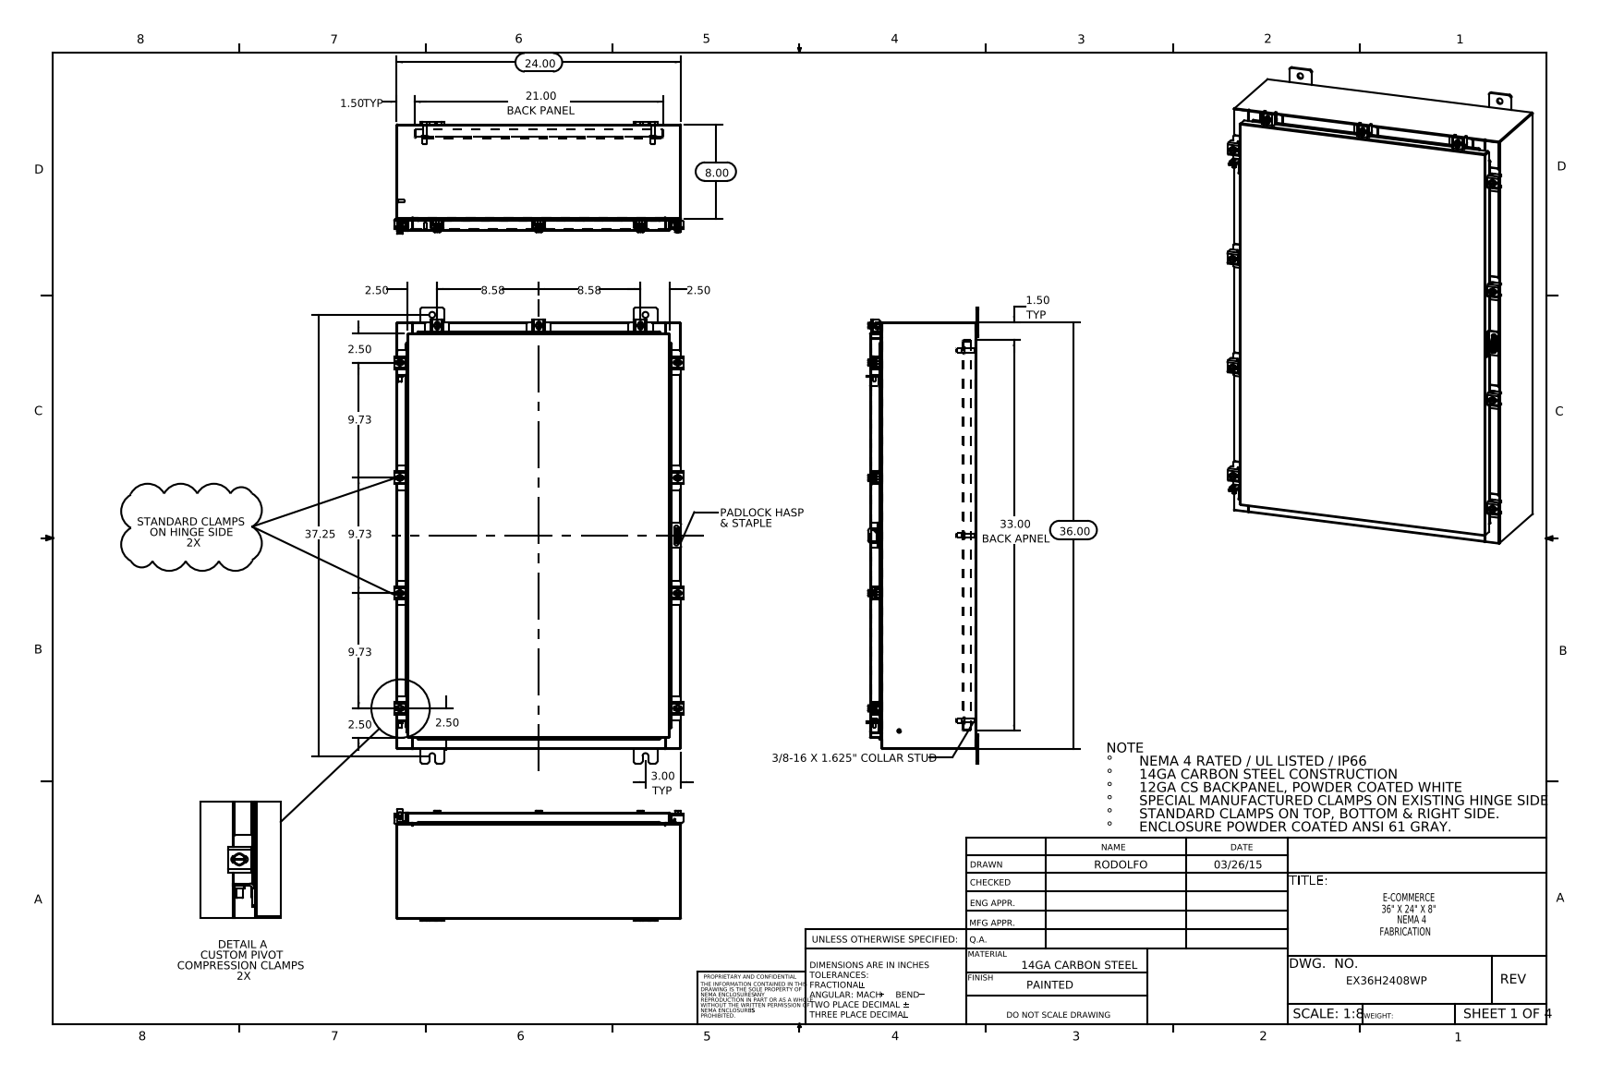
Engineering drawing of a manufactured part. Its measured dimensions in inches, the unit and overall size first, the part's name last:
Units: inches
Overall size (bounding box): 38.5 × 24.421 × 9.453
Round holes (diameter × count): ⌀0.213 ×11, ⌀0.26 ×11, ⌀0.5 ×10, ⌀0.125 ×1, ⌀0.25 ×1
Round bosses / shafts (diameter × count): ⌀0.5 ×11, ⌀0.25 ×11, ⌀0.399 ×9, ⌀0.625 ×6, ⌀0.375 ×6, ⌀0.33 ×6, ⌀0.315 ×2, ⌀0.236 ×2
Partial cylindrical surfaces — rounded edges, fillets, slot ends (radius × count): R0.06 ×48, R0.013 ×26, R0.19 ×24, R0.088 ×22, R0.141 ×22, R0.09 ×20, R0.12 ×20, R0.05 ×19
Main face-to-face distances: 0.075, 8.9, 8.975, 8.826, 0.104, 1, 1.075, 7.826, 7.9, 1.179
Hole centre spacings: 25.389, 5.299, 9.73, 10.964, 14.744, 15.625, 19.459, 20.597
Volume: 308.1 in³ · Surface area: 7 633 in²
Bodies: 78 solids, 1971 faces (1041 planar, 758 cylindrical, 172 other)
Part name (STEP PRODUCT): Special Clamp Assembly; EX36H2408WP Clamp Bracket; EX36H2408WP Padlock Staple; N-WMT04X30402202210-00 22101002 (+8 more)
STEP written by: SolidWorks 2014 (CONFIG_CONTROL_DESIGN)
